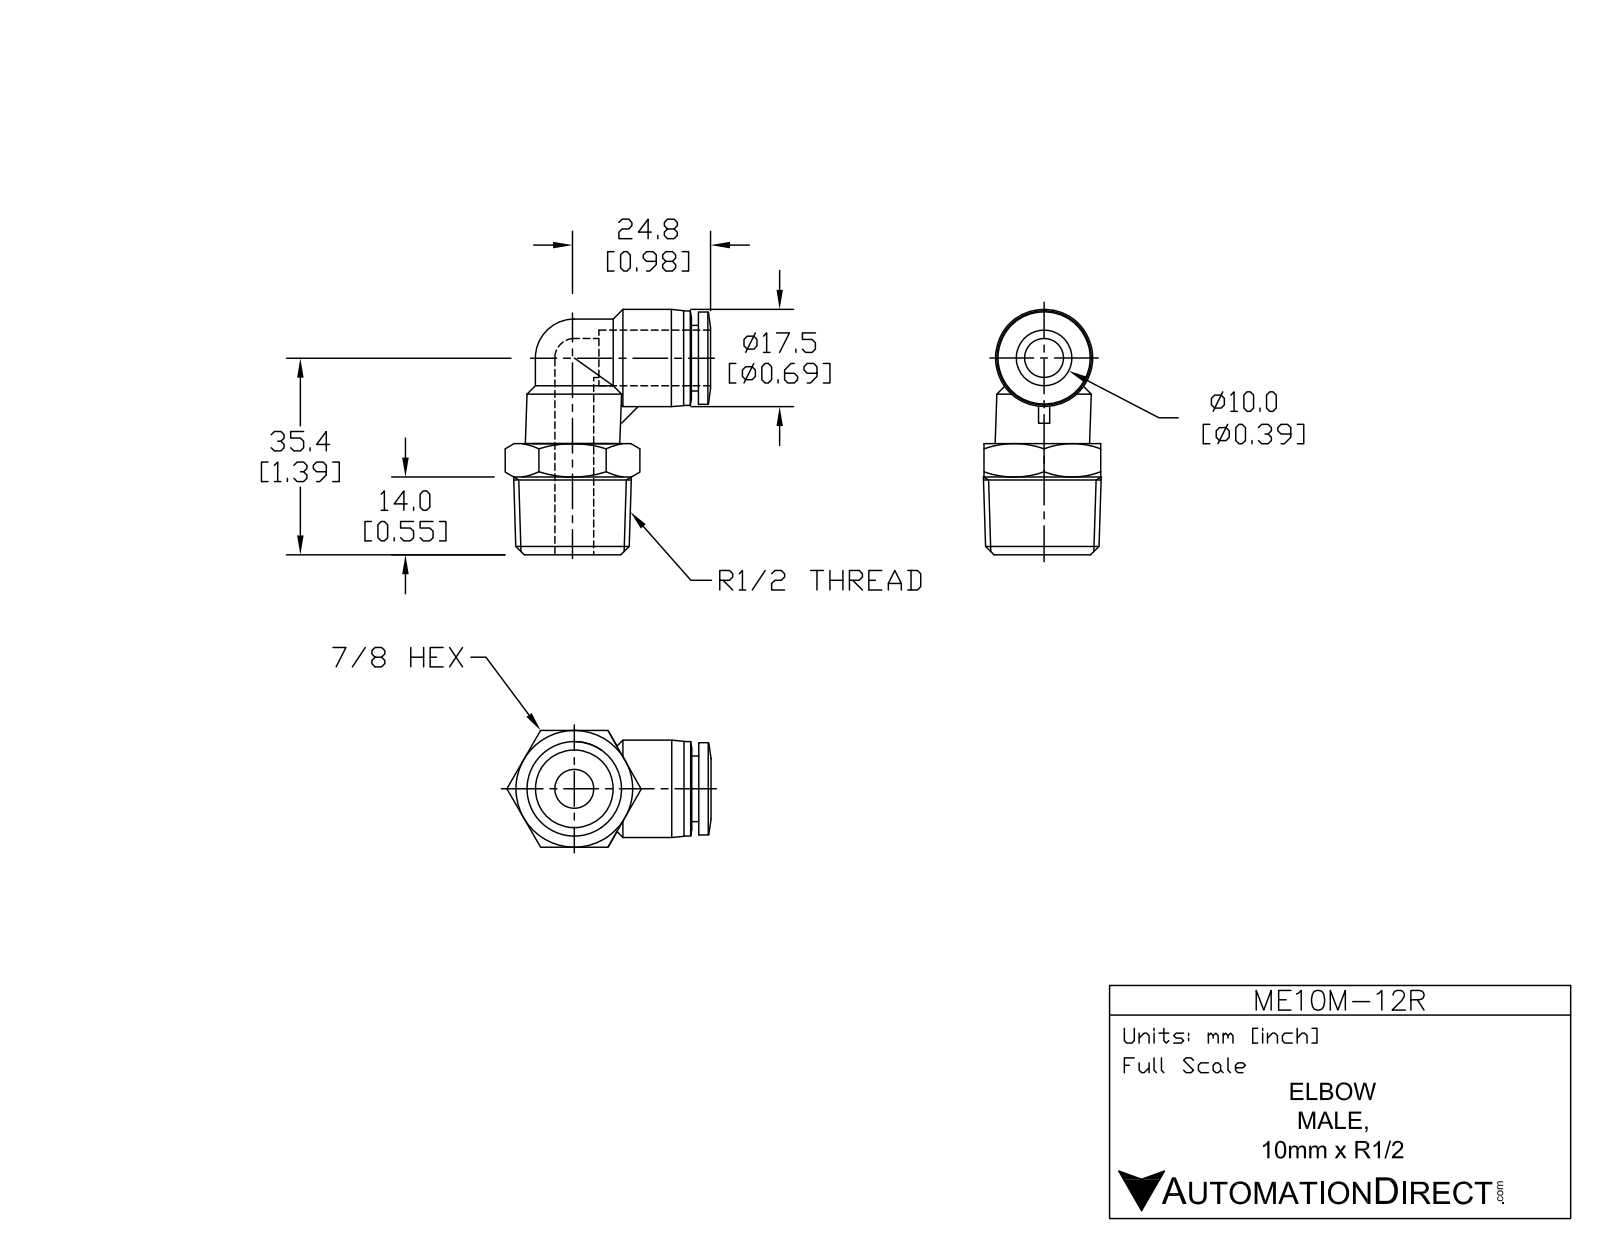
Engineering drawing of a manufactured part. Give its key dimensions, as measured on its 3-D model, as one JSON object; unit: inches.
{"part_name": "ME10M-12R", "step_written_by": "SolidWorks 2015 (AUTOMOTIVE_DESIGN)", "units": "inches", "bodies": {"solids": 1, "faces": 71, "planar": 16, "cylindrical": 20, "other": 35}, "overall_size": [1.742, 1.446, 0.827], "volume_in3": 0.685, "surface_area_in2": 8.872, "round_holes": [[0.315, 2], [0.406, 1]], "round_bosses_or_shafts": [[0.669, 2], [0.689, 1], [0.654, 1], [0.551, 1], [0.465, 1]], "partial_cylinders_radius": [[0.276, 1]], "face_to_face_distances": [0.827, 0.787, 0.049, 0.659, 0.709, 0.374, 0.453, 0.079, 0.604, 0.055]}
